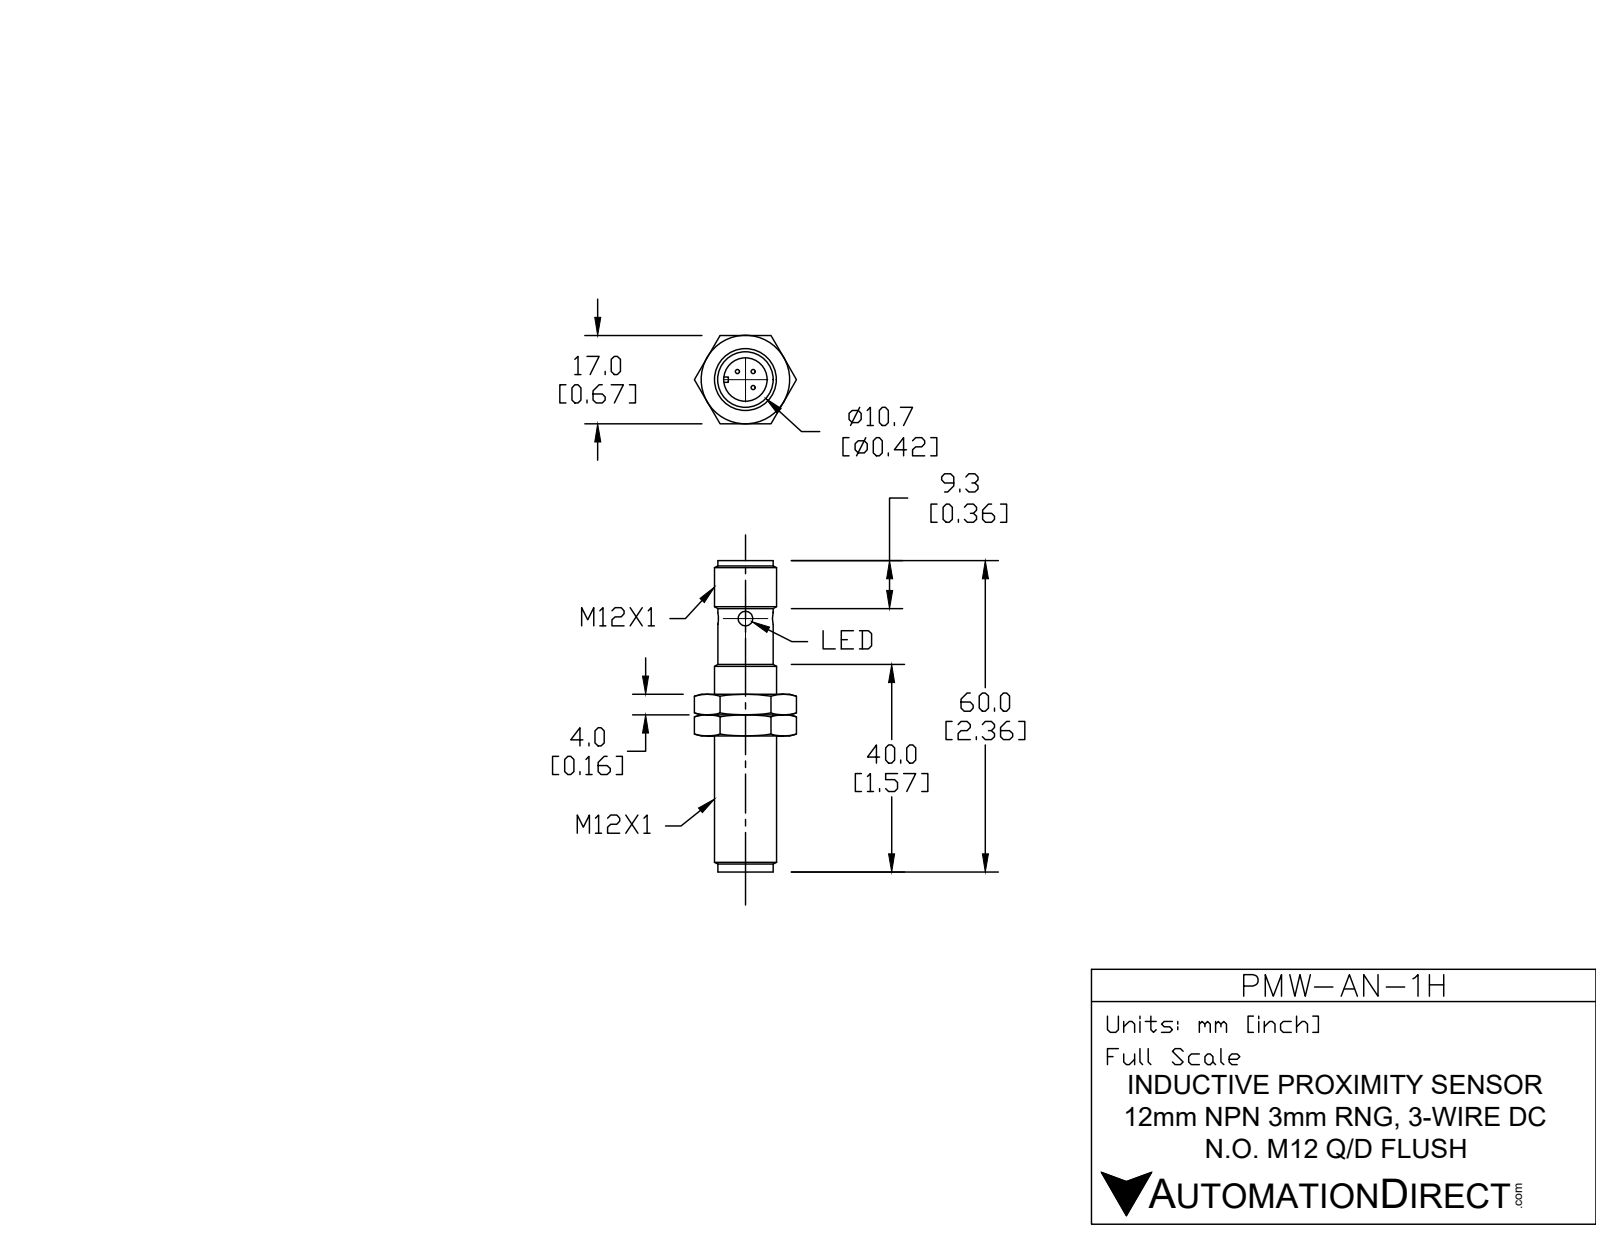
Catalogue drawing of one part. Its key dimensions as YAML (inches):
part_name: "PMW-AN-1H"
step_written_by: "SolidWorks 2017 (AUTOMOTIVE_DESIGN)"
units: inches
bodies: {solids: 3, faces: 100, planar: 26, cylindrical: 32, other: 42}
overall_size: [2.362, 0.773, 0.669]
volume: 0.436
surface_area: 6.196
round_holes:
  - {diameter: 0.098, count: 2}
  - {diameter: 0.331, count: 1}
  - {diameter: 0.43, count: 1}
round_bosses_or_shafts:
  - {diameter: 0.472, count: 1}
  - {diameter: 0.417, count: 1}
  - {diameter: 0.413, count: 1}
  - {diameter: 0.406, count: 1}
partial_cylinders:
  - {radius: 0.024, count: 1}
  - {radius: 0.177, count: 1}
face_to_face_distances: [0.157, 0.669, 0.315, 0.787, 0.63, 0.945, 1.067, 1.224, 1.382, 2.012]
